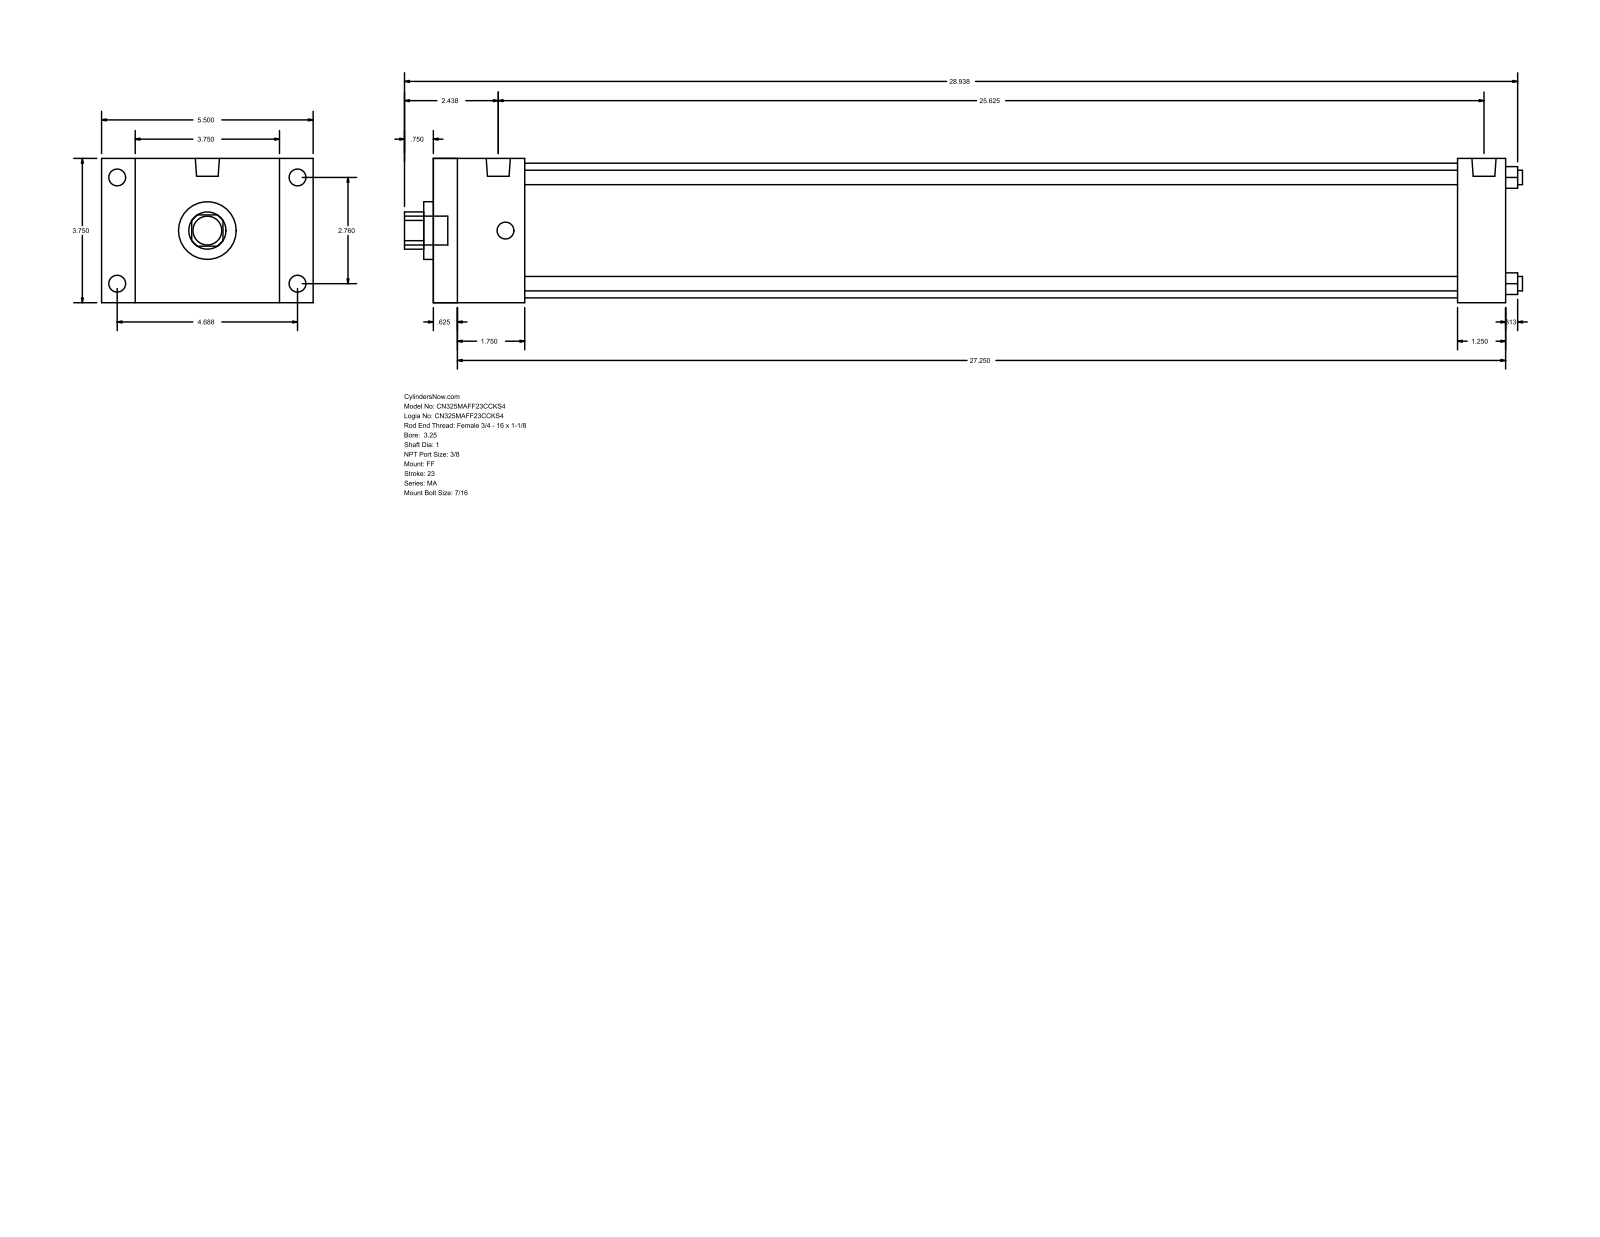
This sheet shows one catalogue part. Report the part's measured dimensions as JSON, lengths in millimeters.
{"part_name": "MA_FF__0325_1", "step_written_by": "GSSL Pune (CONFIG_CONTROL_DESIGN)", "units": "millimeters", "bodies": {"solids": 0, "faces": 92, "planar": 64, "cylindrical": 28, "other": 0}, "overall_size": [738.19, 139.7, 95.25], "round_holes": [[9.53, 4], [25.4, 1], [38.1, 1], [88.9, 1]], "round_bosses_or_shafts": [[11.11, 8], [15.93, 2], [19.05, 1]], "partial_cylinders_radius": [[12.29, 1]], "face_to_face_distances": [95.24, 708.03, 15.87, 692.16, 22.23, 117.47, 60.33, 676.28, 44.46, 660.41], "hole_center_spacings": [49.57, 70.1, 99.14]}
